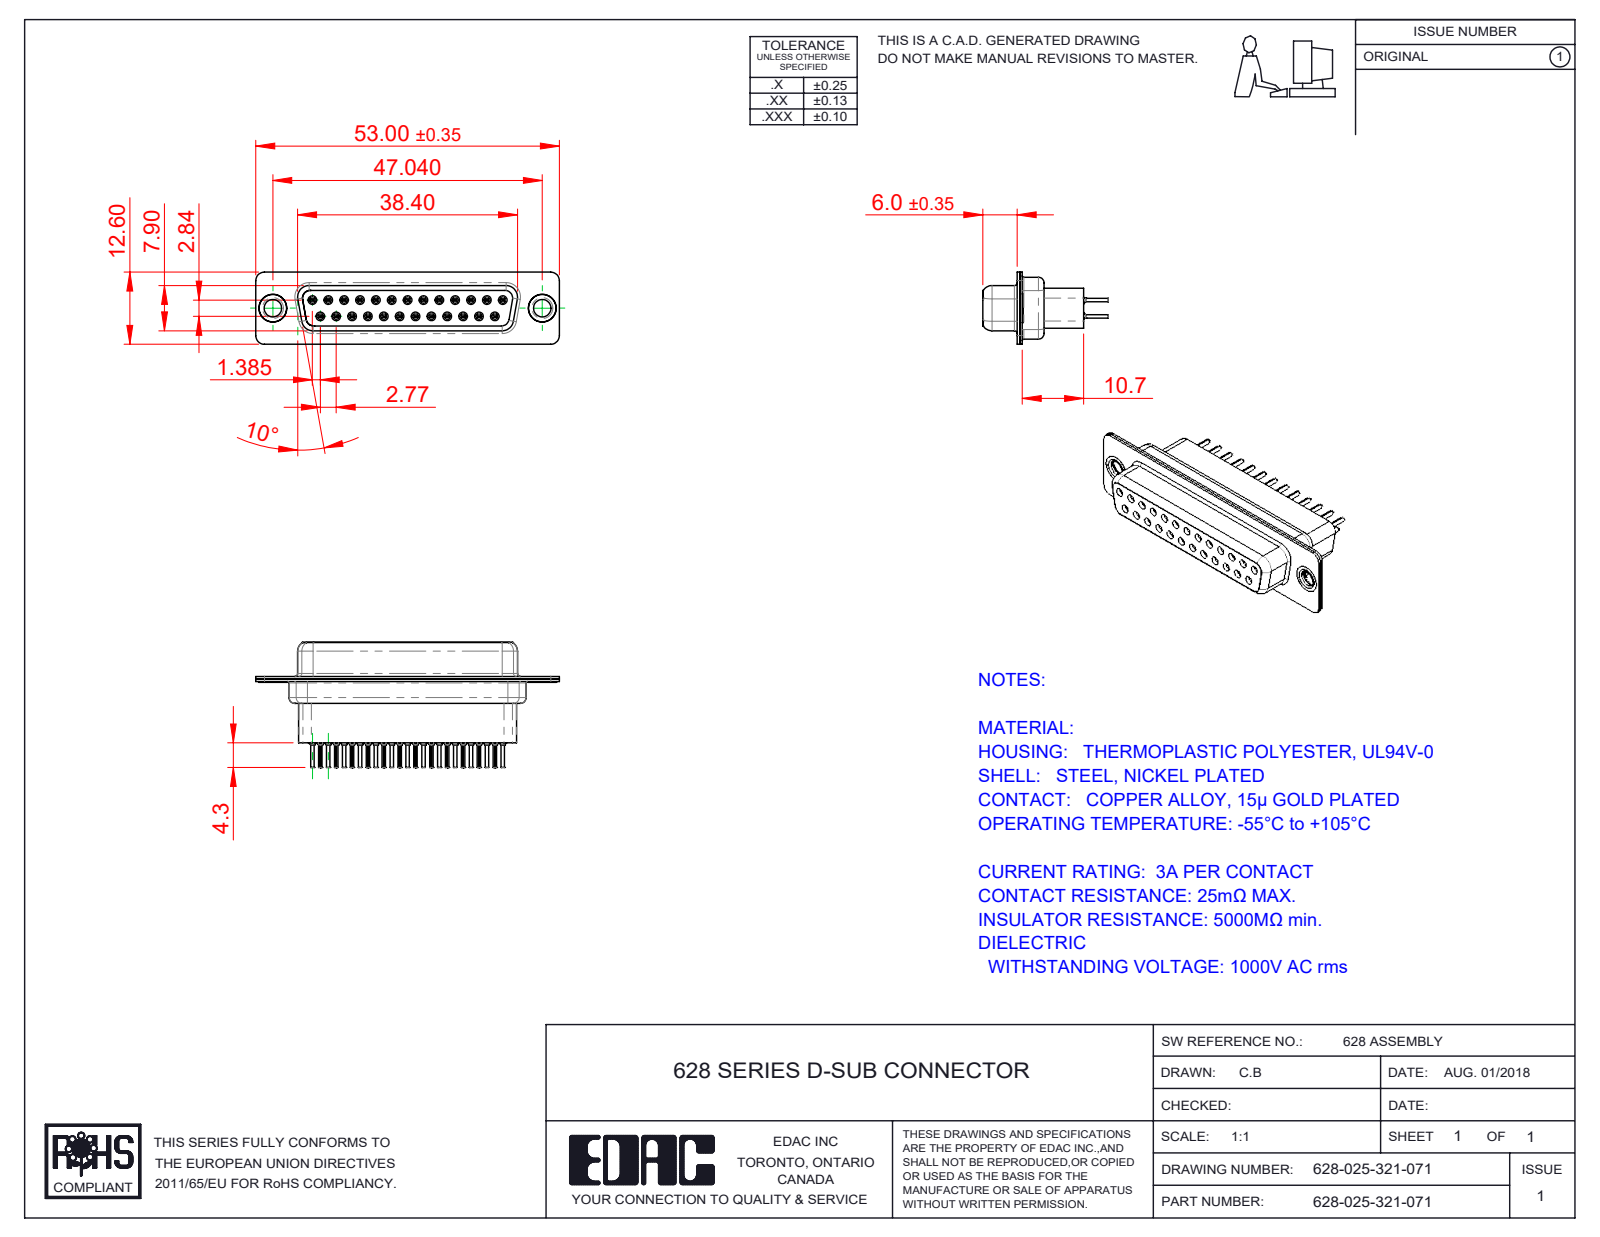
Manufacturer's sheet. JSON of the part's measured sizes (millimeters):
{"part_name": "628-025-321-071; 628 Housing_25 HP; 628 Thru Hole Rivet; 628 Shell Front_25 Contacts (+3 more)", "step_written_by": "SolidWorks 2020 (CONFIG_CONTROL_DESIGN)", "units": "millimeters", "bodies": {"solids": 30, "faces": 3328, "planar": 842, "cylindrical": 946, "other": 1540}, "overall_size": [53, 21.9, 12.6], "volume_mm3": 4908, "surface_area_mm2": 11337, "round_holes": [[0.2, 25], [0.8, 25], [0.9, 25], [1.1, 25], [1.6, 25], [1.7, 13], [3.05, 2], [4, 2], [4.05, 2], [4.85, 2]], "round_bosses_or_shafts": [[2, 25], [1.5, 25], [1.2, 25], [0.6, 25], [5, 2], [4.95, 2], [4.8, 2], [3.55, 2]], "partial_cylinders_radius": [[0.1, 50], [0.28, 25], [1.5, 16], [2, 12], [1.35, 6], [0.25, 4], [0.5, 4], [0.6, 4]], "face_to_face_distances": [0.45, 0.4, 6.6, 8.5, 1.9, 7, 0.9, 7.05, 1.4, 7.45], "hole_center_spacings": [3.16, 8.31, 2.77, 5.54, 11.08, 16.62, 5.03, 5.04]}
